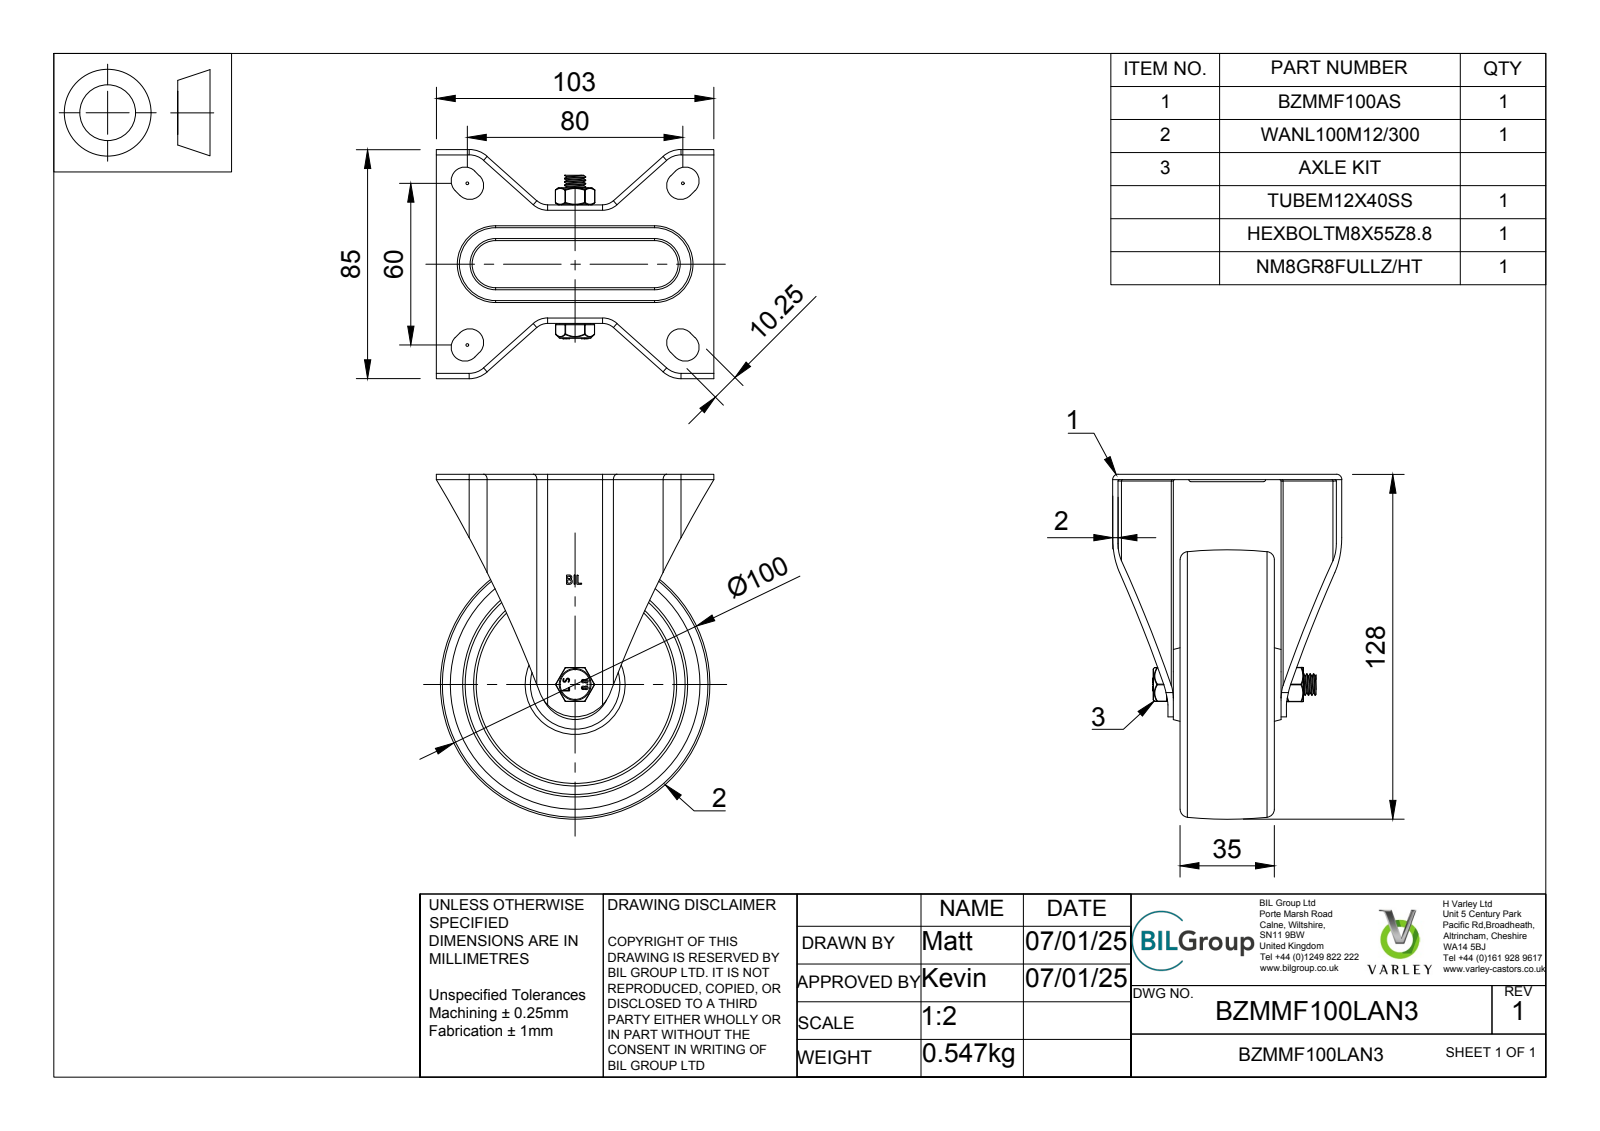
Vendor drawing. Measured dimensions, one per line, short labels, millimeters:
name: BZMMF100LAN3 v3; BZMMF100AS v1; BZMMF100AS; ZINC PLATED, PRESSED STEEL BRACKET (+8 more)
written by: Autodesk Translation Framework v13.20.0.188 (AP242_MANAGED_MODEL_BASED_3D_ENGINEERING_MIM_LF)
unit: mm
bodies: 5 solids, 393 faces (115 planar, 144 cylindrical, 134 other)
size: 128 × 103 × 85
volume: 203 559 mm³; area: 76 661 mm²
holes: 2× ⌀0.66, 1× ⌀8, 1× ⌀8.25, 1× ⌀8.5, 1× ⌀12.5
bosses: 1× ⌀11.9, 1× ⌀11.5, 1× ⌀7.87, 1× ⌀6.45
rounds: 18× R0.25, 8× R0.5, 8× R0.75, 8× R2, 8× R5.12, 4× R0.33, 4× R0.64, 4× R3
face distances: 2, 14.26, 15.5, 24.5, 17.5, 26.5, 42, 9, 12.26, 16.26
hole spacings: 3.22, 2.49
